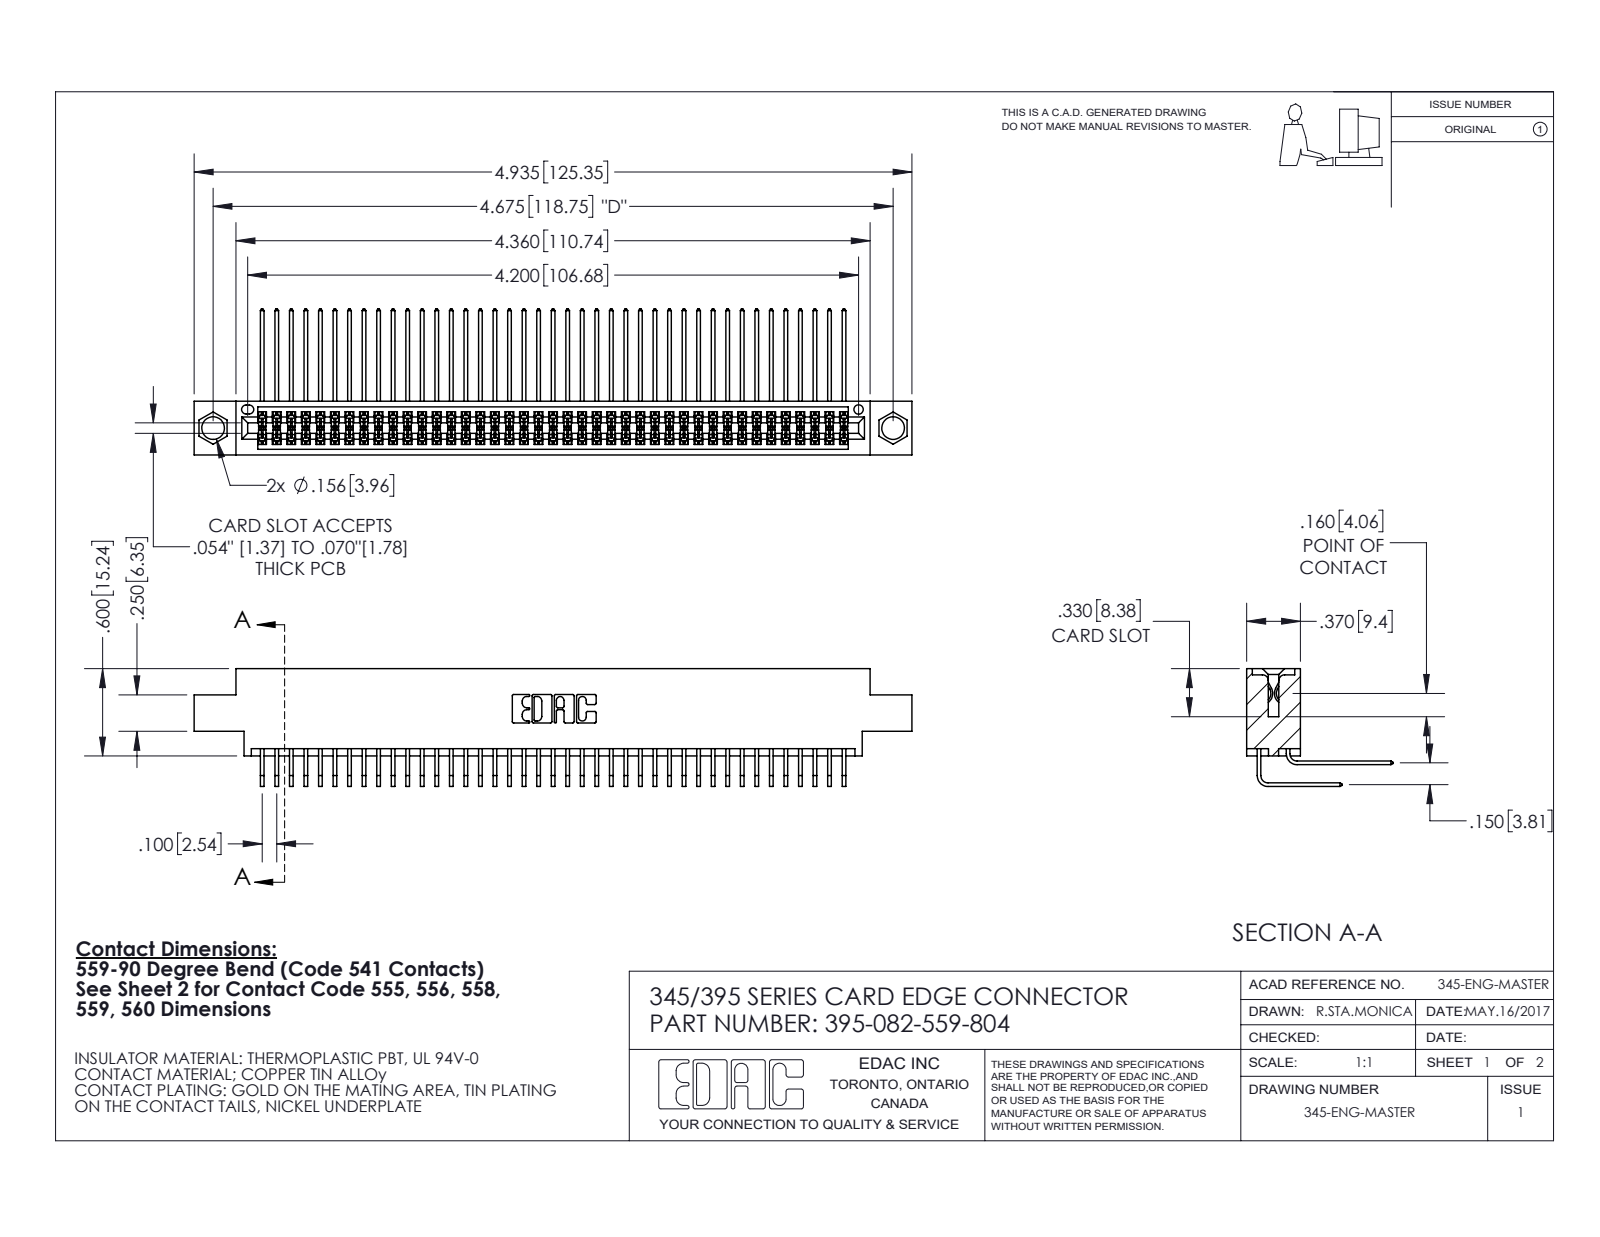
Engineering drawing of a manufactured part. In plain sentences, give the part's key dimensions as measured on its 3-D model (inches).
The part is named "345-292-001_558 559 Tail - 1; 345-292-001_559 Tail - 2; 345 Part_0.170 Offset - 0.156 Dia-TI; 395-082-559-804". Its 3-D file was written by "SolidWorks 2020 (CONFIG_CONTROL_DESIGN)". It is 83 solids with 4408 faces: 2968 planar, 1440 cylindrical and 0 other. Overall it measures 4.935 by 1.005 by 0.809 inches. Its volume is 0.758 cubic inches and its surface area 31.87 square inches. Round holes: 2 of diameter 0.156, 1 of diameter 0.064. Partial cylindrical surfaces (rounded edges, fillets, slot ends): 123 of radius 0.006, 22 of radius 0.01, 6 of radius 0.007, 6 of radius 0.031, 3 of radius 0.026, 2 of radius 0.014, 2 of radius 0.019, 2 of radius 0.022. The main face-to-face distances are 0.072, 0.298, 0.37, 0.2, 0.098, 0.272, 0.025, 0.225, 0.175, 0.15. The hole center spacings are 0.27, 4.439, 4.675.
